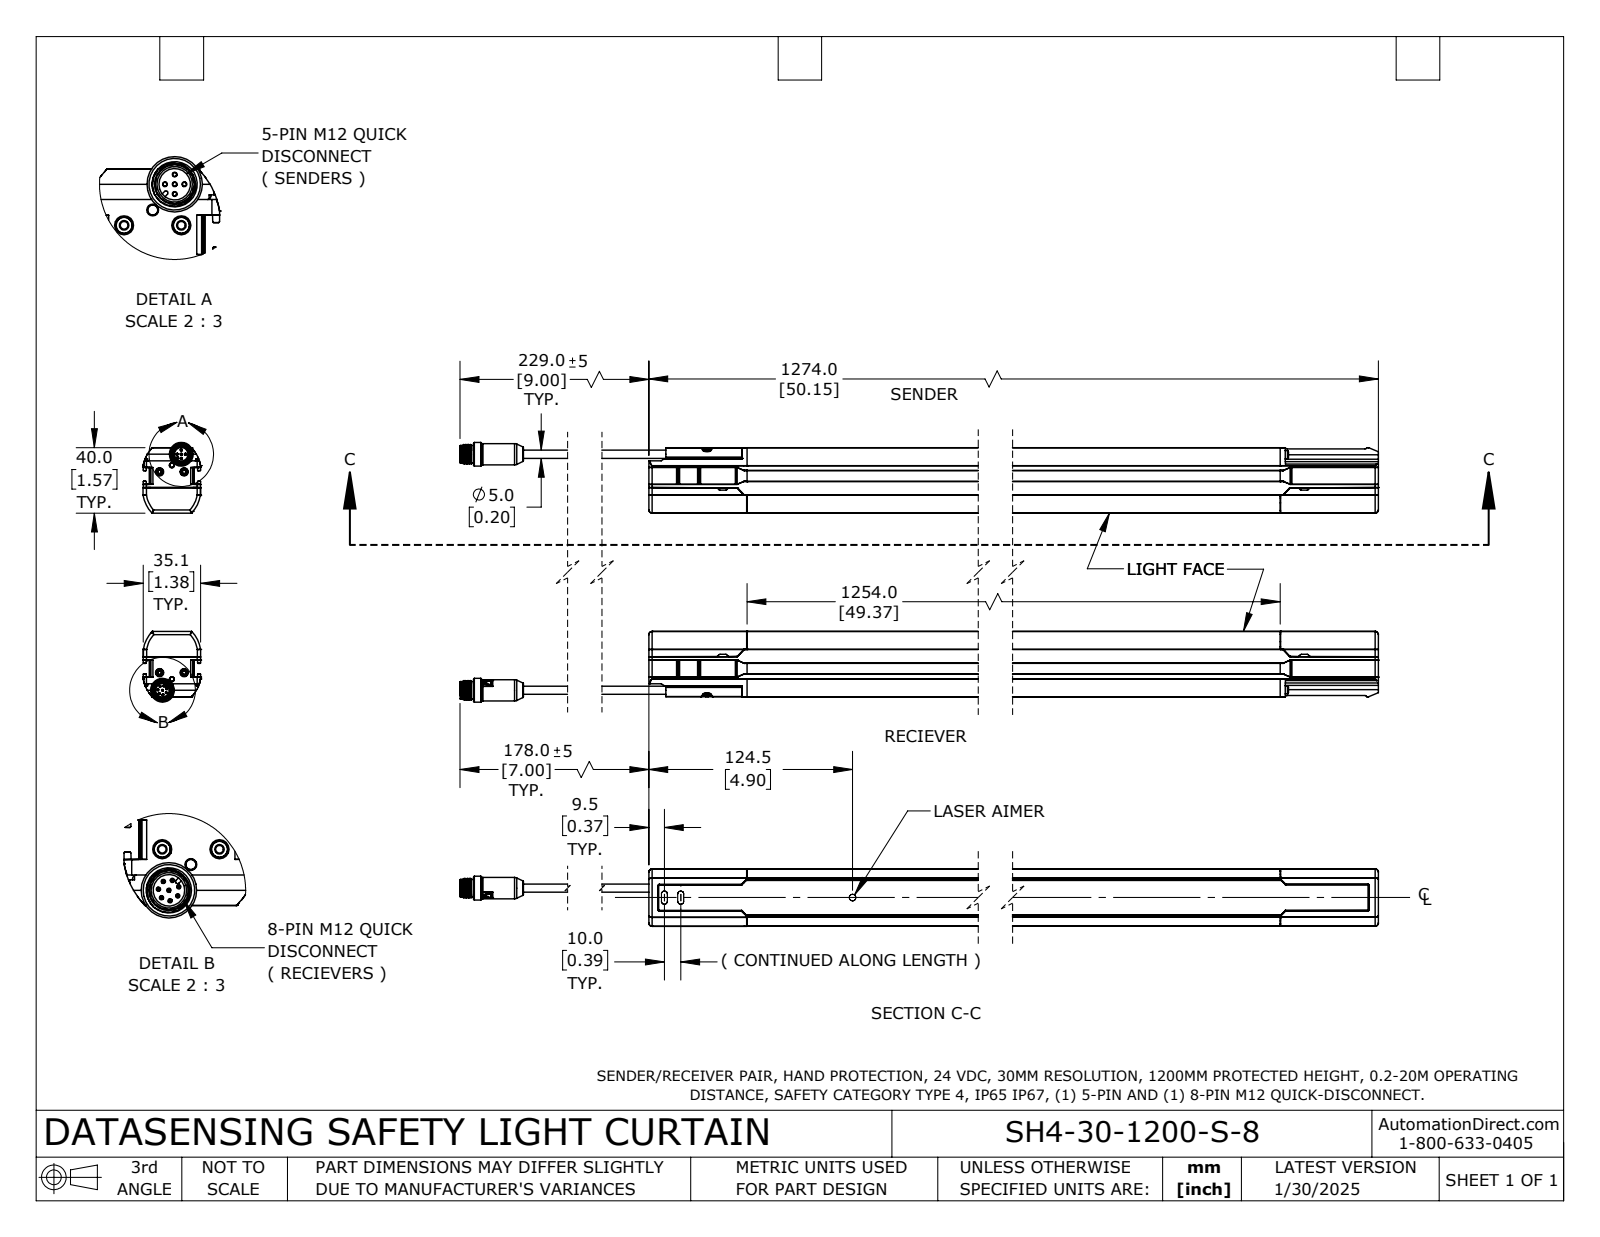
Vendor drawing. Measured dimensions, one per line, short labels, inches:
name: 957920063
written by: SolidWorks 2024 (AUTOMOTIVE_DESIGN)
unit: in
bodies: 4 solids, 2608 faces (1186 planar, 784 cylindrical, 638 other)
size: 56.587 × 6.248 × 1.384
volume: 174.1 in³; area: 755.3 in²
holes: 4× ⌀0.079, 4× ⌀0.101, 4× ⌀0.118, 4× ⌀0.197, 2× ⌀0.101, 2× ⌀0.102, 2× ⌀0.325, 2× ⌀0.382, 2× ⌀0.407, 2× ⌀0.425, 1× ⌀0.11, 1× ⌀0.138
bosses: 10× ⌀0.197, 8× ⌀0.087, 8× ⌀0.031, 5× ⌀0.039, 4× ⌀0.172, 2× ⌀0.571, 2× ⌀0.512, 2× ⌀0.417
rounds: 164× R0.01, 66× R0.016, 50× R0.02, 36× R0.008, 20× R0.031, 12× R0.031, 12× R0.079, 10× R0.059
face distances: 1.496, 4.496, 0.156, 1.222, 3, 5.992, 1.378, 1.067, 4.634, 1.033
hole spacings: 0.866, 5.27, 5.34, 0.429, 0.591, 0.672, 4.831, 4.867
